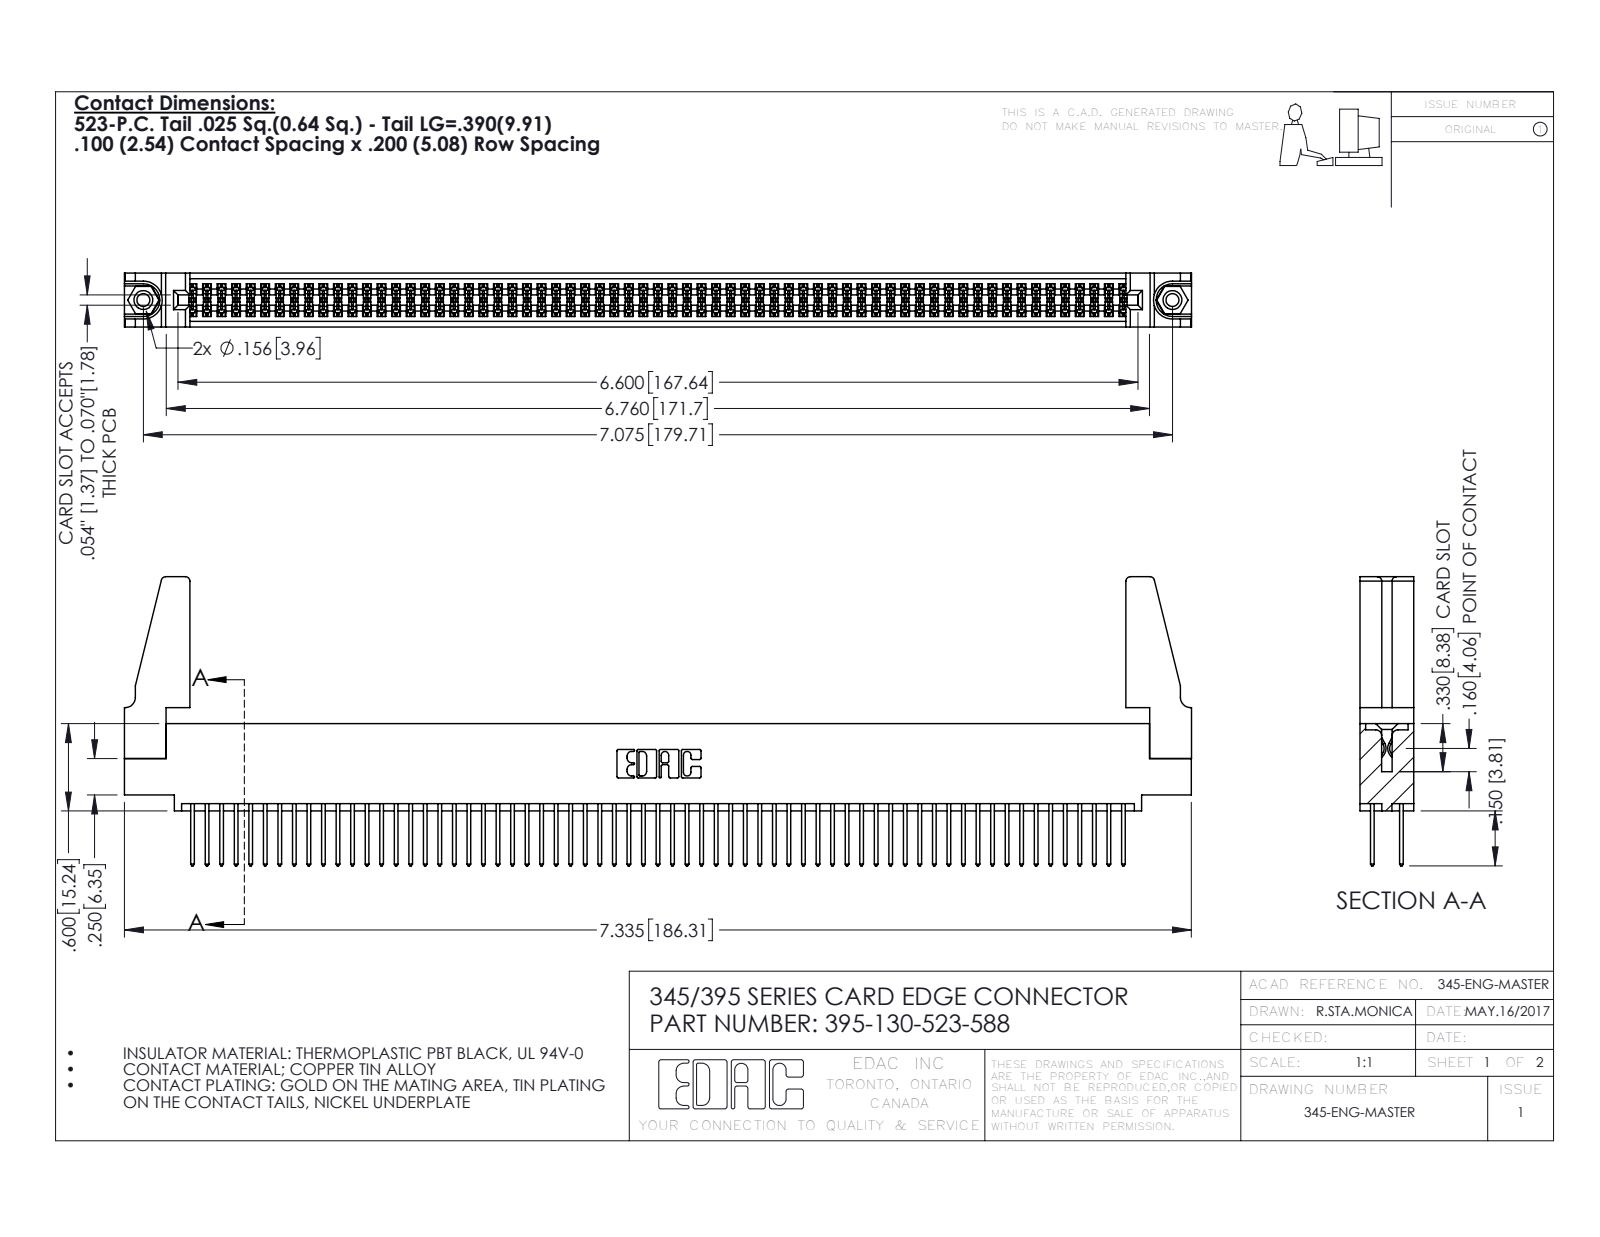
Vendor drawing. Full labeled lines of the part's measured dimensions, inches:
Part name (STEP PRODUCT): 345-220-078_345-220-088; 345-250-001_345-250-001-102; 345-292-001_345-293-123; 345 Part_0.110 Offset - 0.156 Dia-TH (+1 more)
STEP written by: SolidWorks 2016 (CONFIG_CONTROL_DESIGN)
Units: inches
Bodies: 135 solids, 6754 faces (4446 planar, 2292 cylindrical, 16 other)
Overall size (bounding box): 7.336 × 1.987 × 0.37
Volume: 1.328 in³ · Surface area: 49.93 in²
Round holes (diameter × count): ⌀0.089 ×2, ⌀0.125 ×2, ⌀0.156 ×2, ⌀0.064 ×1
Round bosses / shafts (diameter × count): ⌀0.155 ×2
Partial cylindrical surfaces — rounded edges, fillets, slot ends (radius × count): R0.006 ×195, R0.01 ×130, R0.01 ×22, R0.03 ×8, R0.007 ×6, R0.031 ×6, R0.026 ×3, R0.014 ×2
Main face-to-face distances: 0.072, 0.298, 0.2, 0.098, 0.272, 0.025, 0.37, 0.225, 0.175, 0.149
Hole centre spacings: 0.27, 6.839, 7.075
